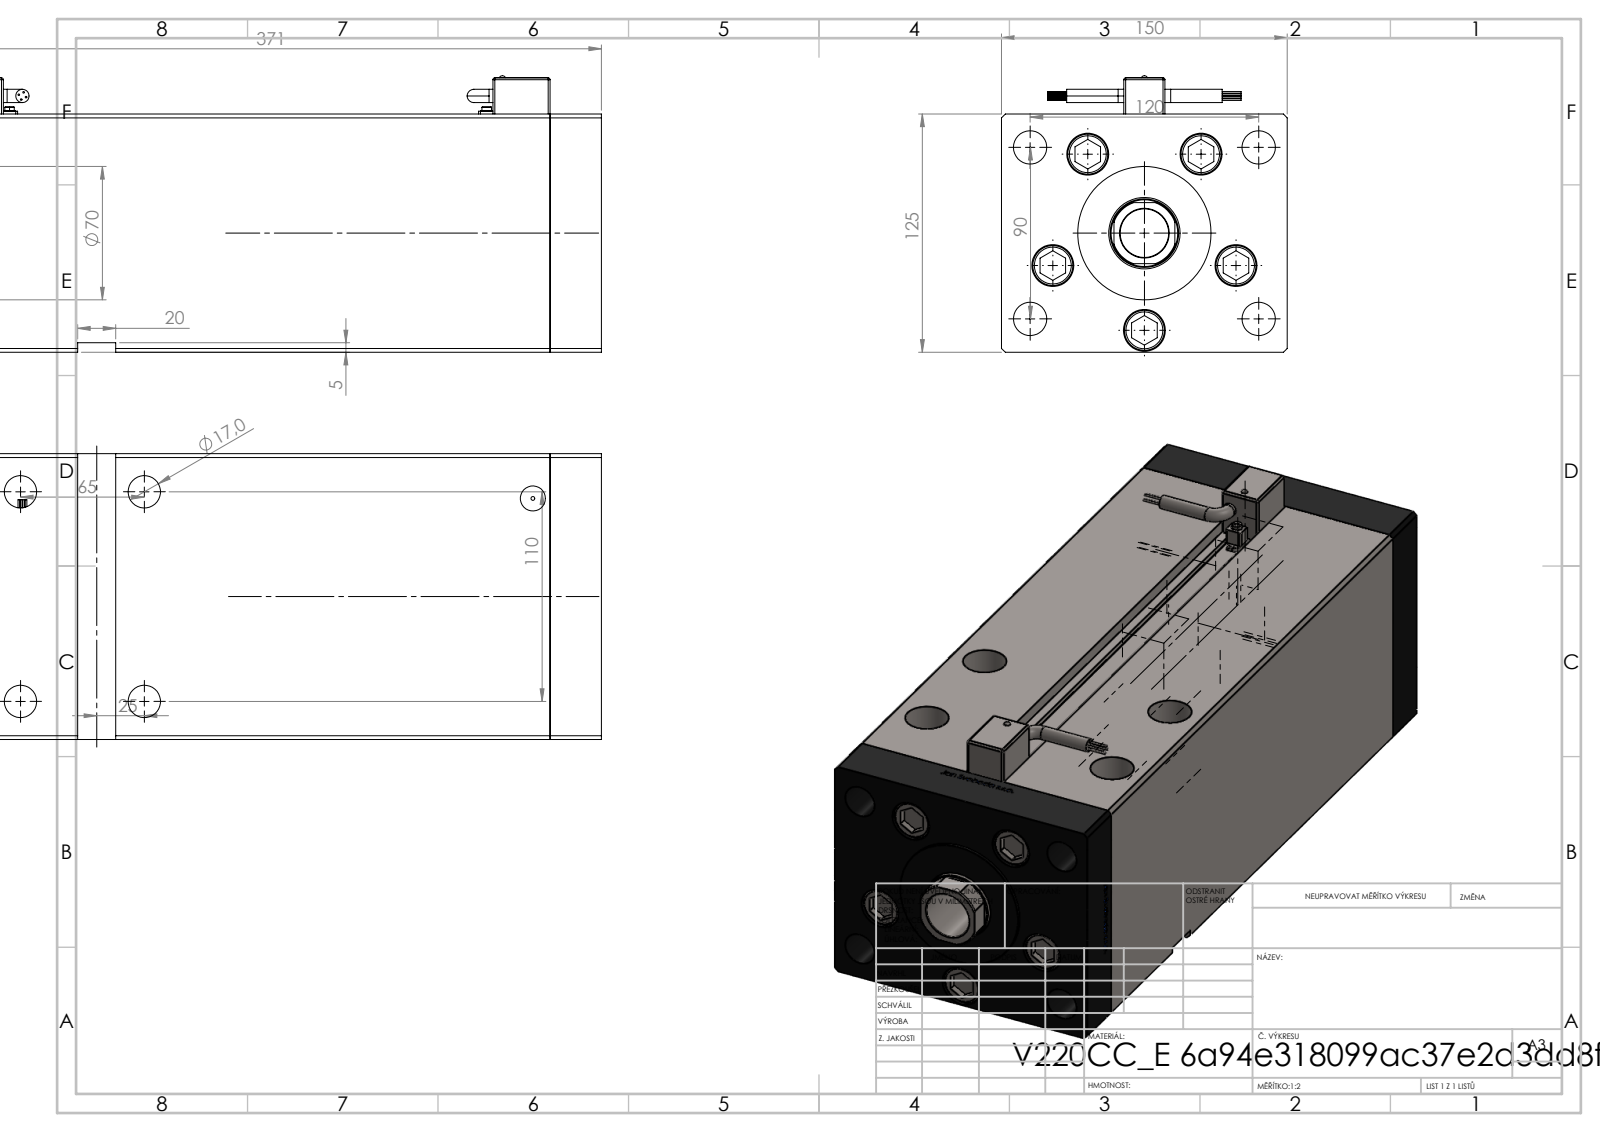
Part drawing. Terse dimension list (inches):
name: V220C_FRONT_E; ALLEN BOLT; V220C_E MIDDLE; V220C_VC_E (+2 more)
written by: SolidWorks 2019 (CONFIG_CONTROL_DESIGN)
unit: in
bodies: 16 solids, 1418 faces (553 planar, 255 cylindrical, 610 other)
size: 15.197 × 5.906 × 5.713
volume: 344.2 in³; area: 850 in²
holes: 9× ⌀0.689, 5× ⌀0.866, 4× ⌀0.669, 4× ⌀0.906, 2× ⌀0.079, 2× ⌀0.142, 2× ⌀0.197, 2× ⌀0.276, 2× ⌀0.518, 1× ⌀1.004, 1× ⌀1.417, 1× ⌀1.476
bosses: 8× ⌀0.033, 5× ⌀0.827, 5× ⌀0.315, 4× ⌀0.276, 2× ⌀0.236, 2× ⌀0.138, 2× ⌀0.098, 1× ⌀3.15
rounds: 24× R0.039, 4× R0.157, 2× R0.037, 1× R0.689
face distances: 4.921, 5.906, 1.063, 12.48, 13.543, 0.256, 1.319, 14.606, 12.224, 13.287
hole spacings: 2.008, 2.953, 0.325, 1.198, 1.2, 2.123, 2.177, 2.234
